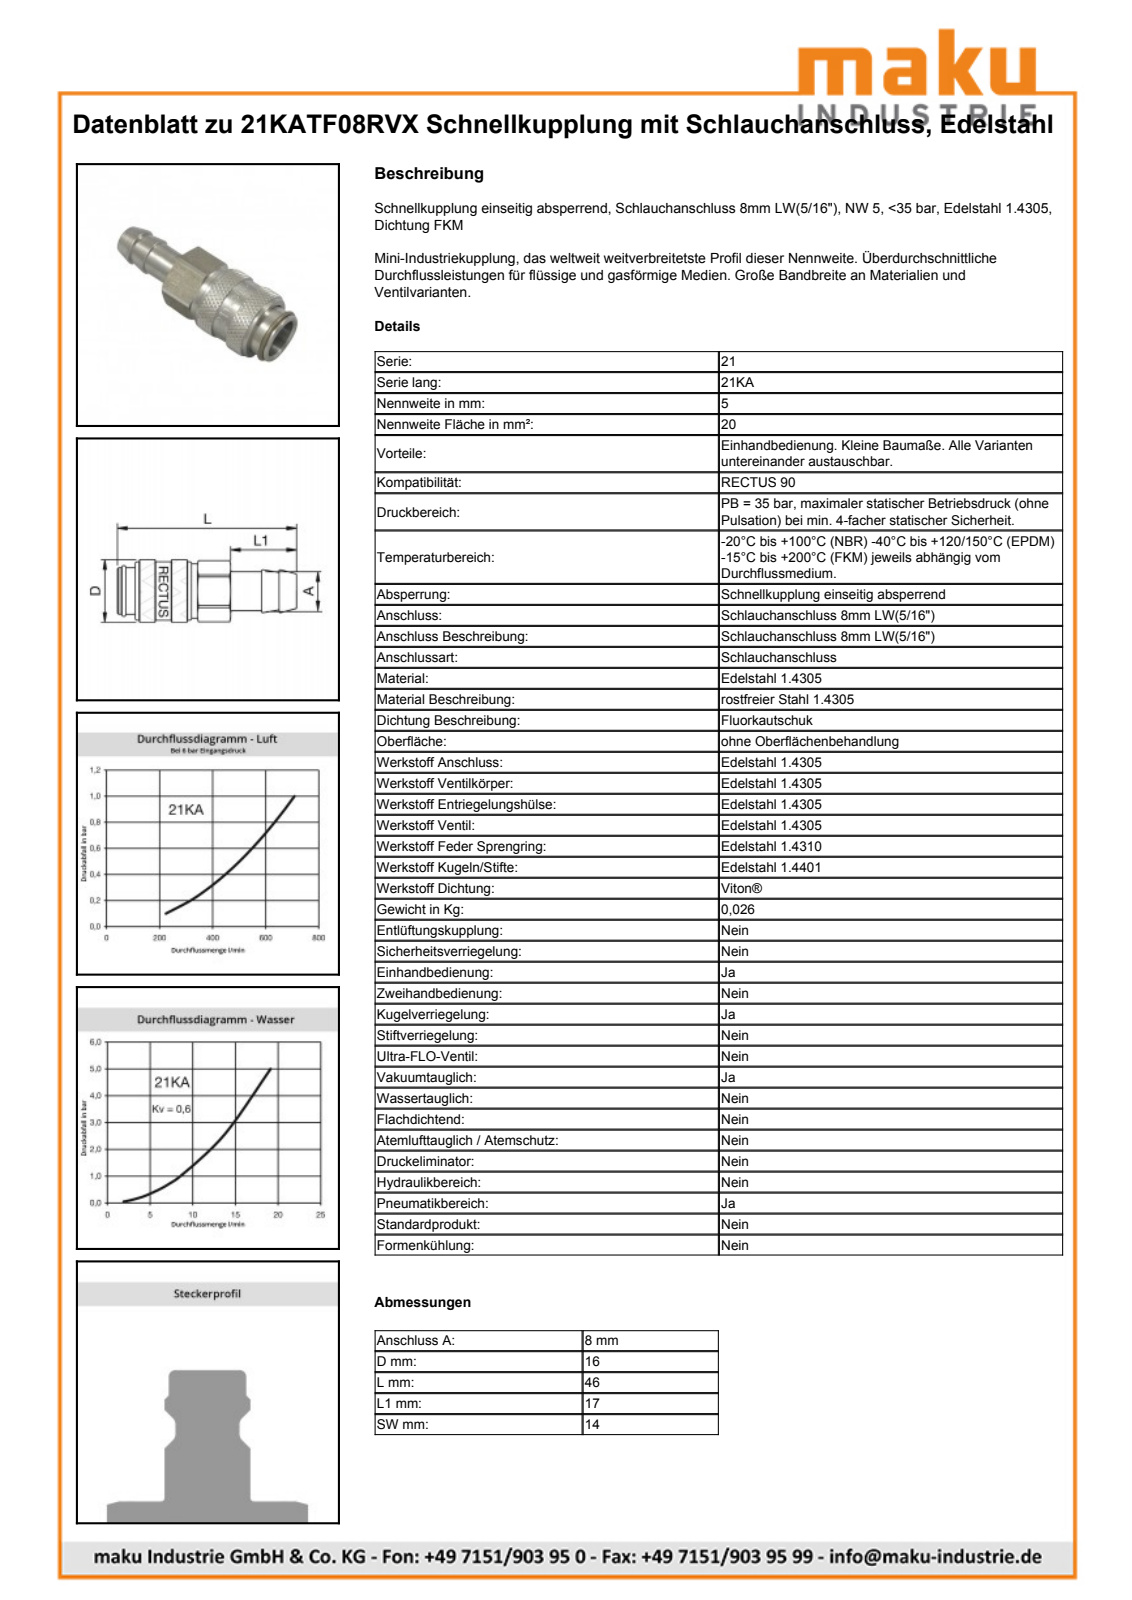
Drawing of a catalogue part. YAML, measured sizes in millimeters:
part_name: "D103793"
step_written_by: "Autodesk Inventor 2011 (AUTOMOTIVE_DESIGN)"
units: millimeters
bodies: {solids: 2, faces: 494, planar: 197, cylindrical: 60, other: 237}
overall_size: [46.15, 16.15, 16.15]
volume: 5605
surface_area: 3628
round_holes:
  - {diameter: 12.15, count: 1}
  - {diameter: 14, count: 1}
round_bosses_or_shafts:
  - {diameter: 16.15, count: 1}
  - {diameter: 15.1, count: 1}
  - {diameter: 12, count: 1}
  - {diameter: 11.4, count: 1}
  - {diameter: 11.15, count: 1}
  - {diameter: 8.05, count: 1}
partial_cylinders:
  - {radius: 5.56, count: 1}
  - {radius: 7.45, count: 1}
  - {radius: 7.9, count: 1}
face_to_face_distances: [14, 29.15, 16.15, 13, 4.56, 11.59, 24.59, 11.86, 7.3, 4.29]
